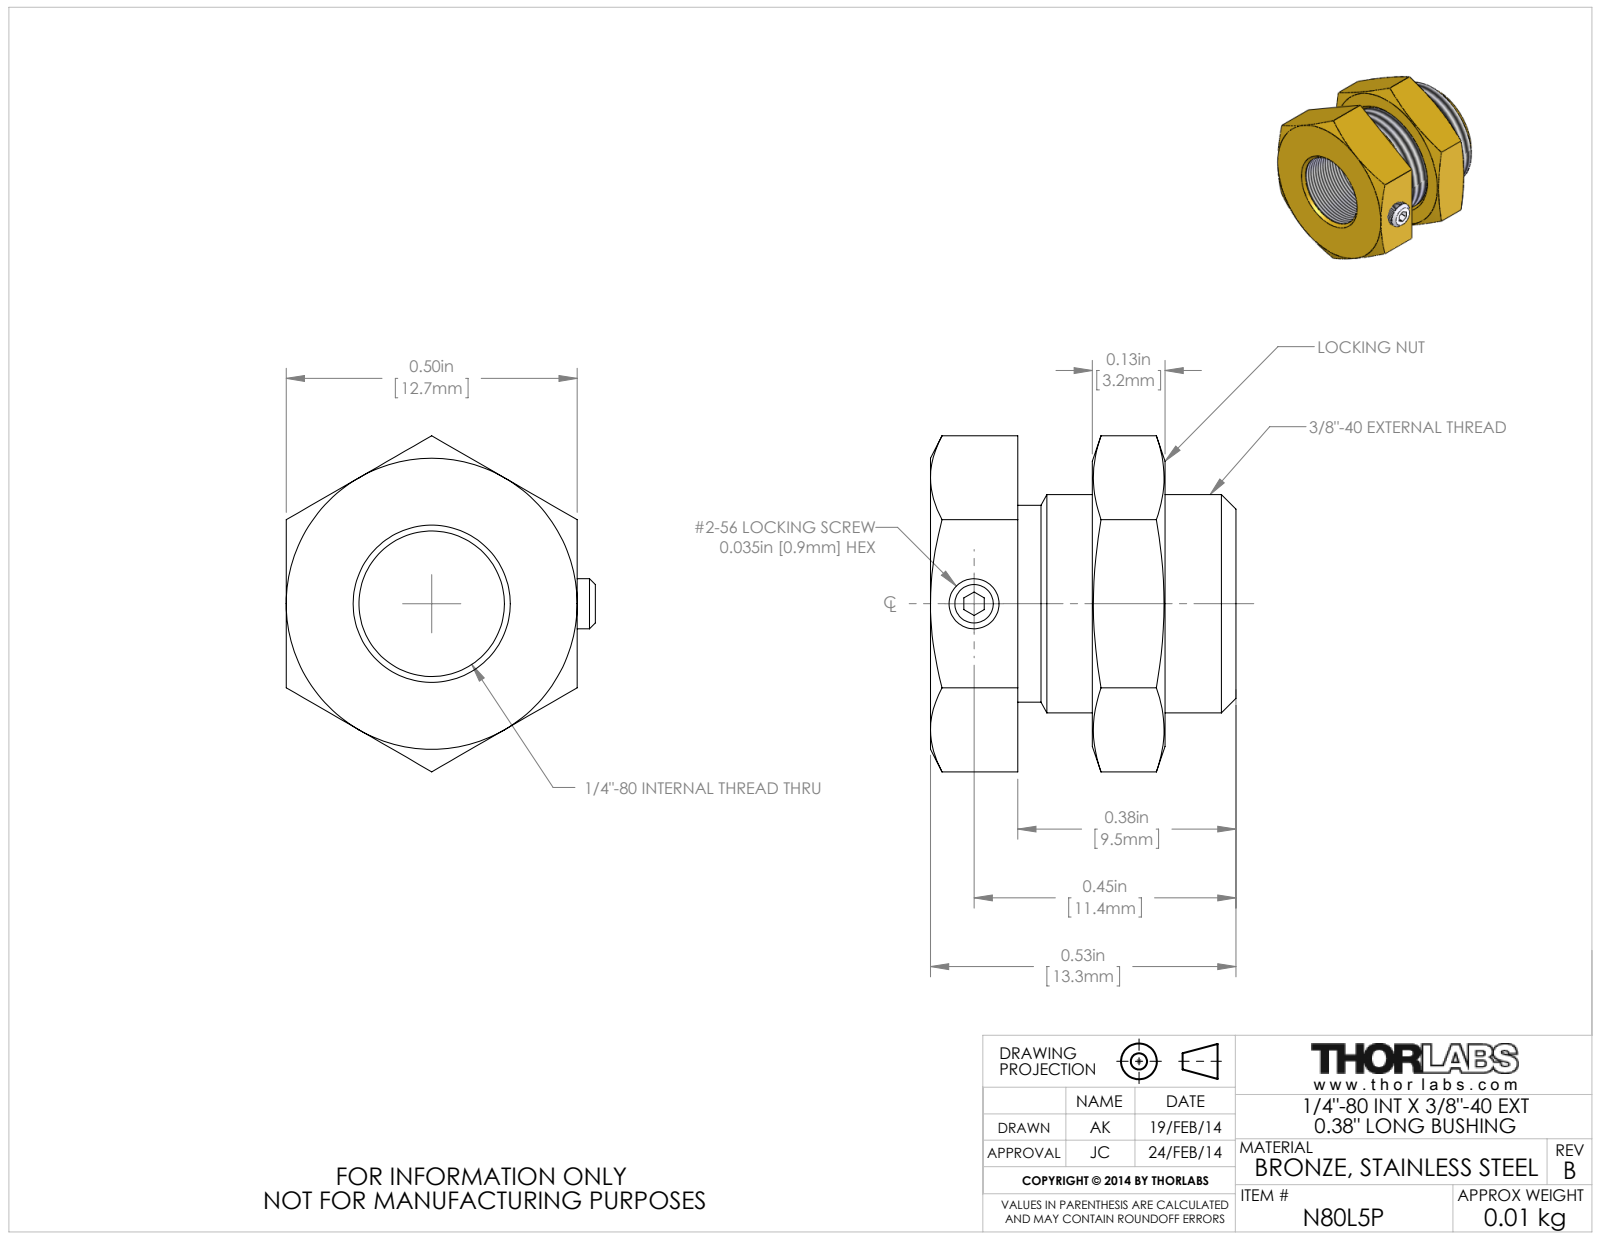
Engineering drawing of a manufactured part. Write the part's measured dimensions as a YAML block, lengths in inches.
part_name: "19449-E0W"
step_written_by: "SolidWorks 2007 (AUTOMOTIVE_DESIGN)"
units: inches
bodies: {solids: 3, faces: 69, planar: 27, cylindrical: 14, other: 28}
overall_size: [0.577, 0.531, 0.525]
volume: 0.06
surface_area: 2.054
round_holes:
  - {diameter: 0.07, count: 1}
  - {diameter: 0.25, count: 1}
  - {diameter: 0.375, count: 1}
round_bosses_or_shafts:
  - {diameter: 0.338, count: 1}
  - {diameter: 0.086, count: 1}
  - {diameter: 0.031, count: 1}
face_to_face_distances: [0.5, 0.15, 0.125, 0.254, 0.404, 0.128, 0.278, 0.122, 0.247, 0.375]
